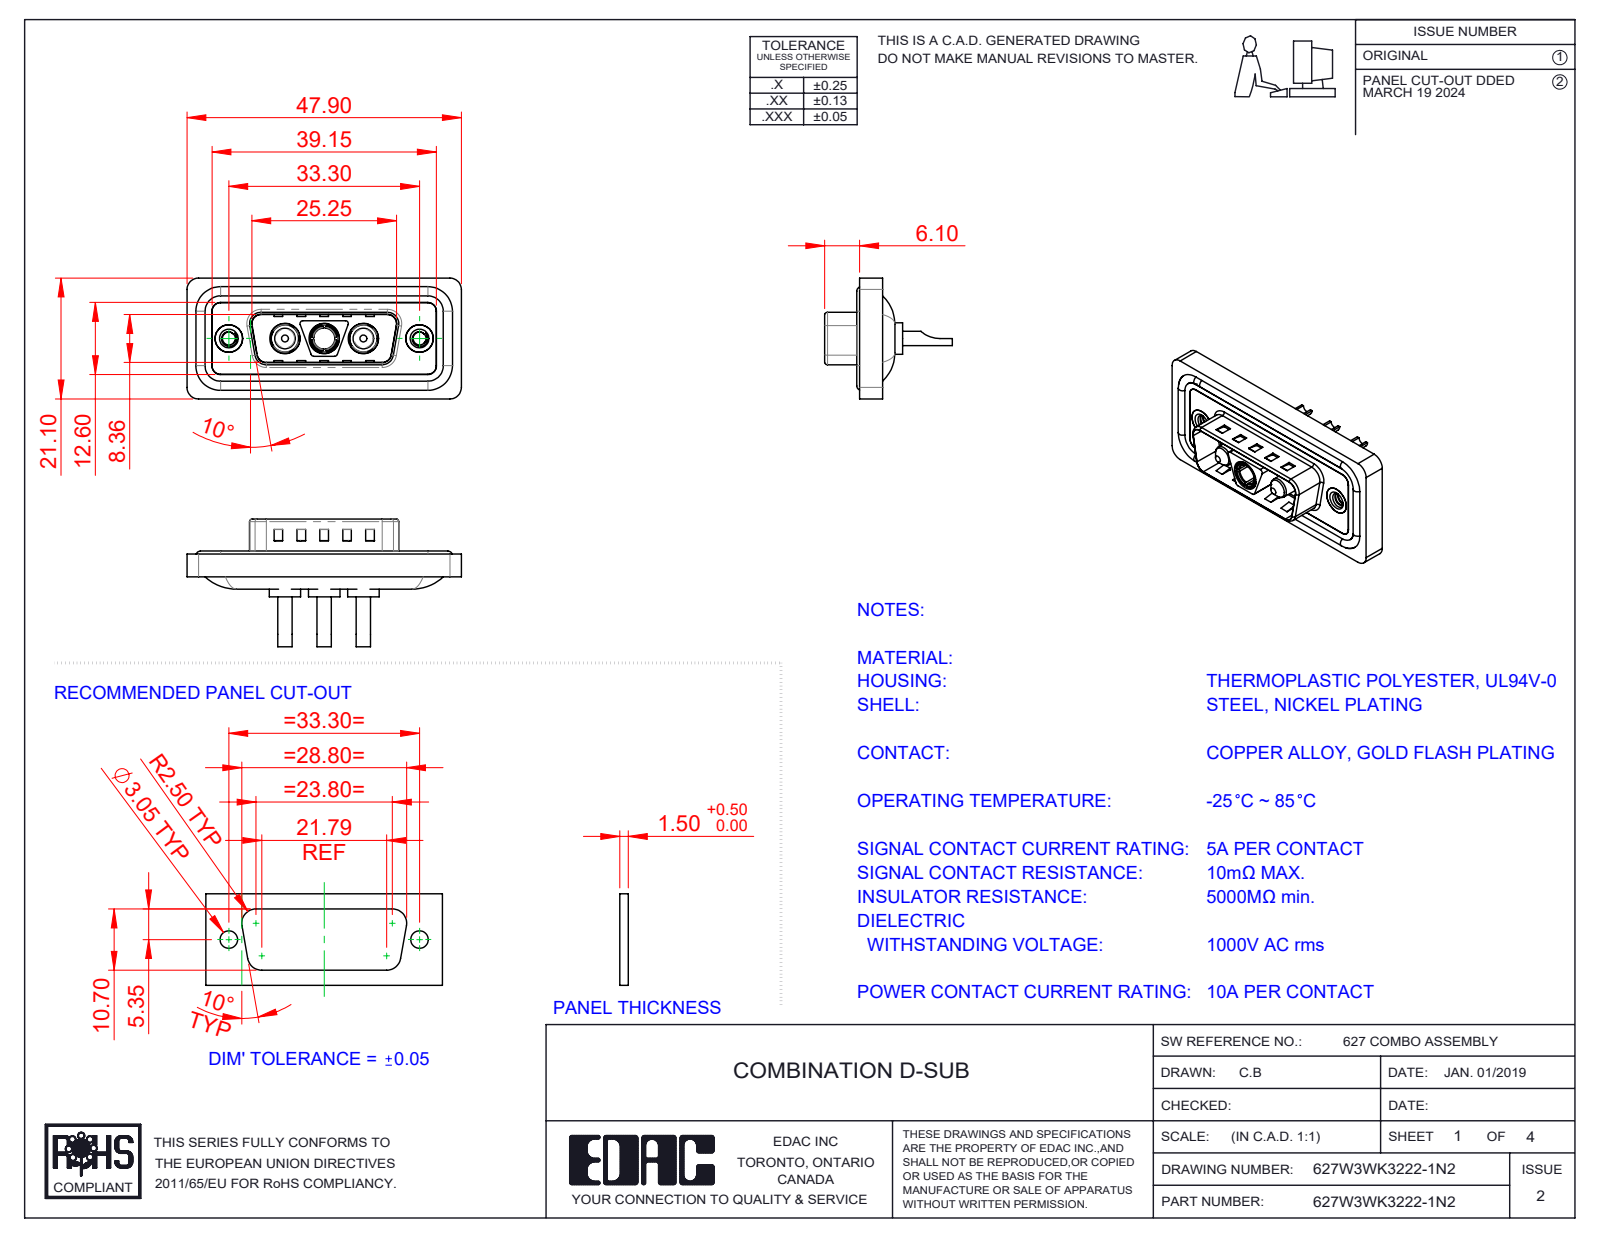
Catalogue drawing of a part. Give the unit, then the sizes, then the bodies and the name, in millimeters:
Units: millimetres
Overall size (bounding box): 47.9 × 22.3 × 21.1
Round holes (diameter × count): ⌀1.7 ×3, ⌀4.85 ×3, ⌀5.3 ×3, ⌀2.26 ×2, ⌀4 ×2, ⌀4.8 ×2, ⌀5 ×2, ⌀3.7 ×1
Round bosses / shafts (diameter × count): ⌀1.6 ×4, ⌀5.5 ×3, ⌀5.2 ×3, ⌀4.75 ×3, ⌀3.75 ×3, ⌀2.5 ×3, ⌀4.9 ×2, ⌀3.6 ×2
Partial cylindrical surfaces — rounded edges, fillets, slot ends (radius × count): R1.5 ×26, R2 ×20, R0.5 ×12, R1.6 ×8, R0.25 ×4, R0.6 ×4, R0.65 ×4, R0.9 ×4
Main face-to-face distances: 0.4, 1.1, 1.5, 0.5, 1.6, 3.1, 2.9, 4, 0.82, 9.58
Hole centre spacings: 6.85, 9.8, 16.65, 23.5, 13.7, 33.3
Volume: 5 680 mm³ · Surface area: 9 270 mm²
Bodies: 13 solids, 627 faces (237 planar, 259 cylindrical, 131 other)
Part name (STEP PRODUCT): Power Pin_10A SC; 627W3WK3222-1N2; 627Combo Waterproof Housing_15 Contacts; 627Combo Housing_3WK3 (+4 more)
STEP written by: SolidWorks 2023 (CONFIG_CONTROL_DESIGN)
